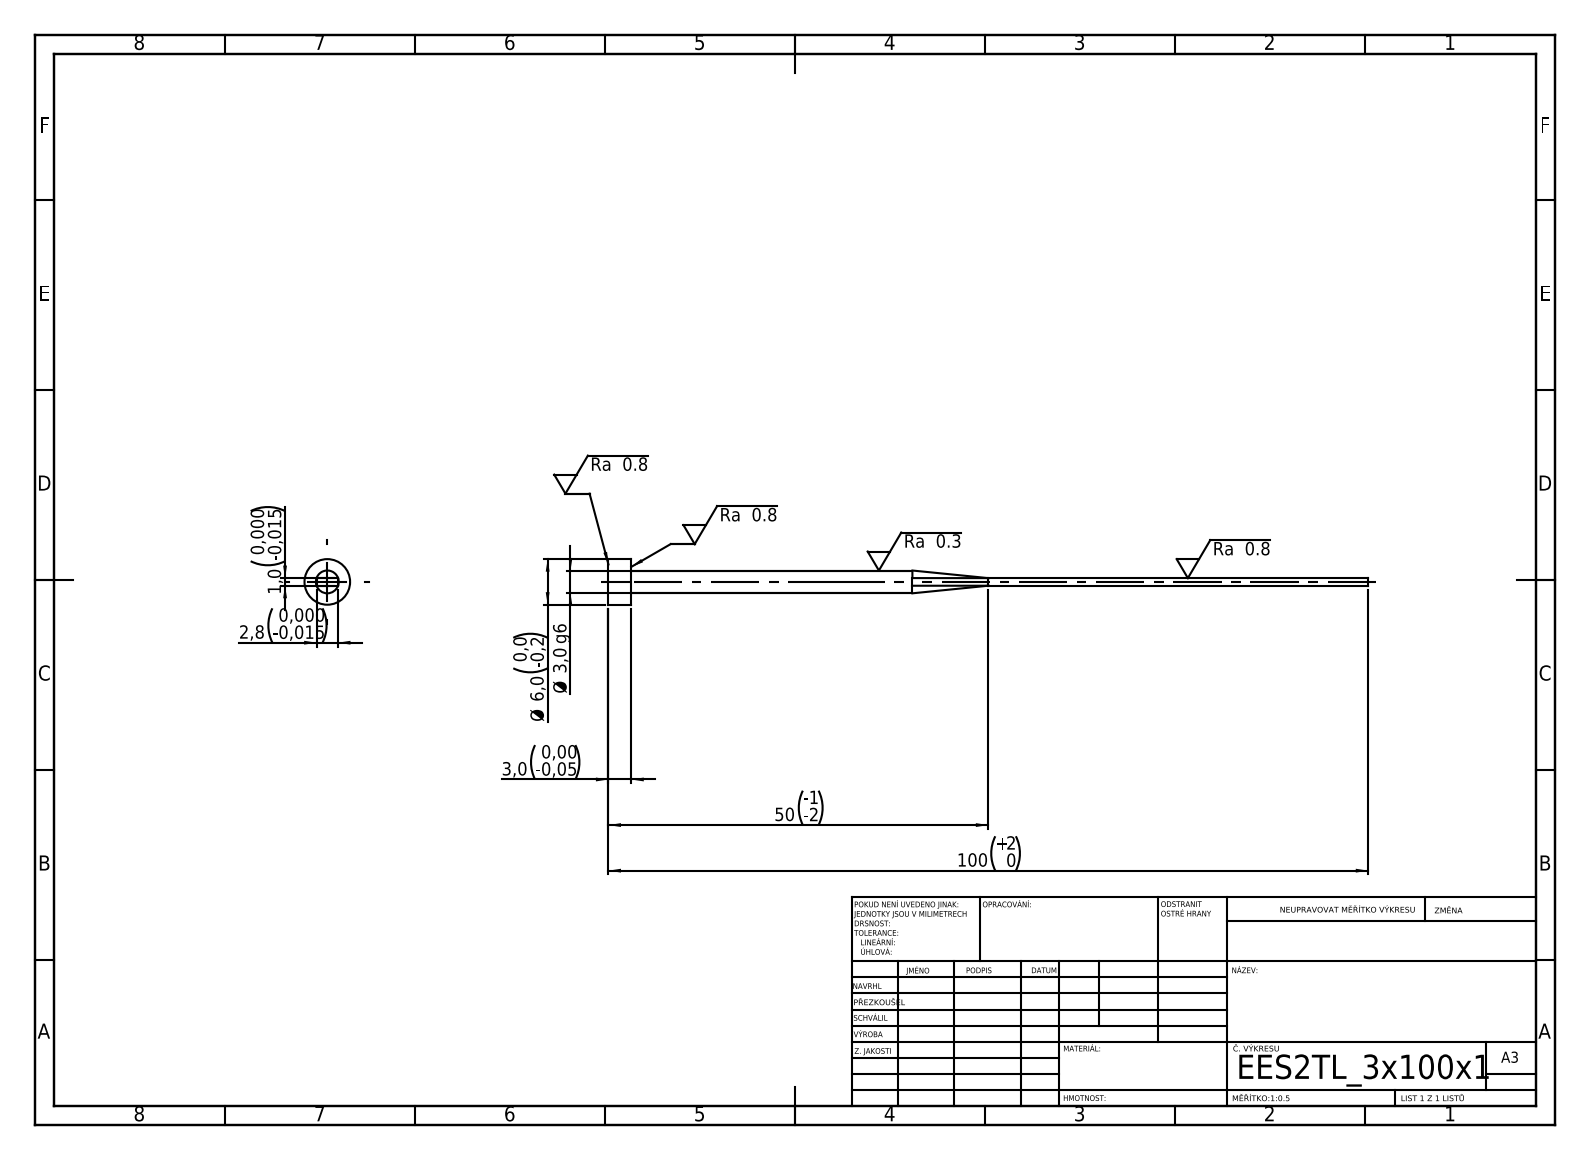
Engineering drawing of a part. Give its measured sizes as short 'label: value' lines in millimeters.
written by: SolidWorks 2019 (CONFIG_CONTROL_DESIGN)
unit: mm
bodies: 1 solid, 15 faces (7 planar, 4 cylindrical, 4 other)
size: 100 × 6 × 6
volume: 535 mm³; area: 920 mm²
bosses: 1× ⌀6, 1× ⌀3
face distances: 1, 2.8, 3, 100, 97
